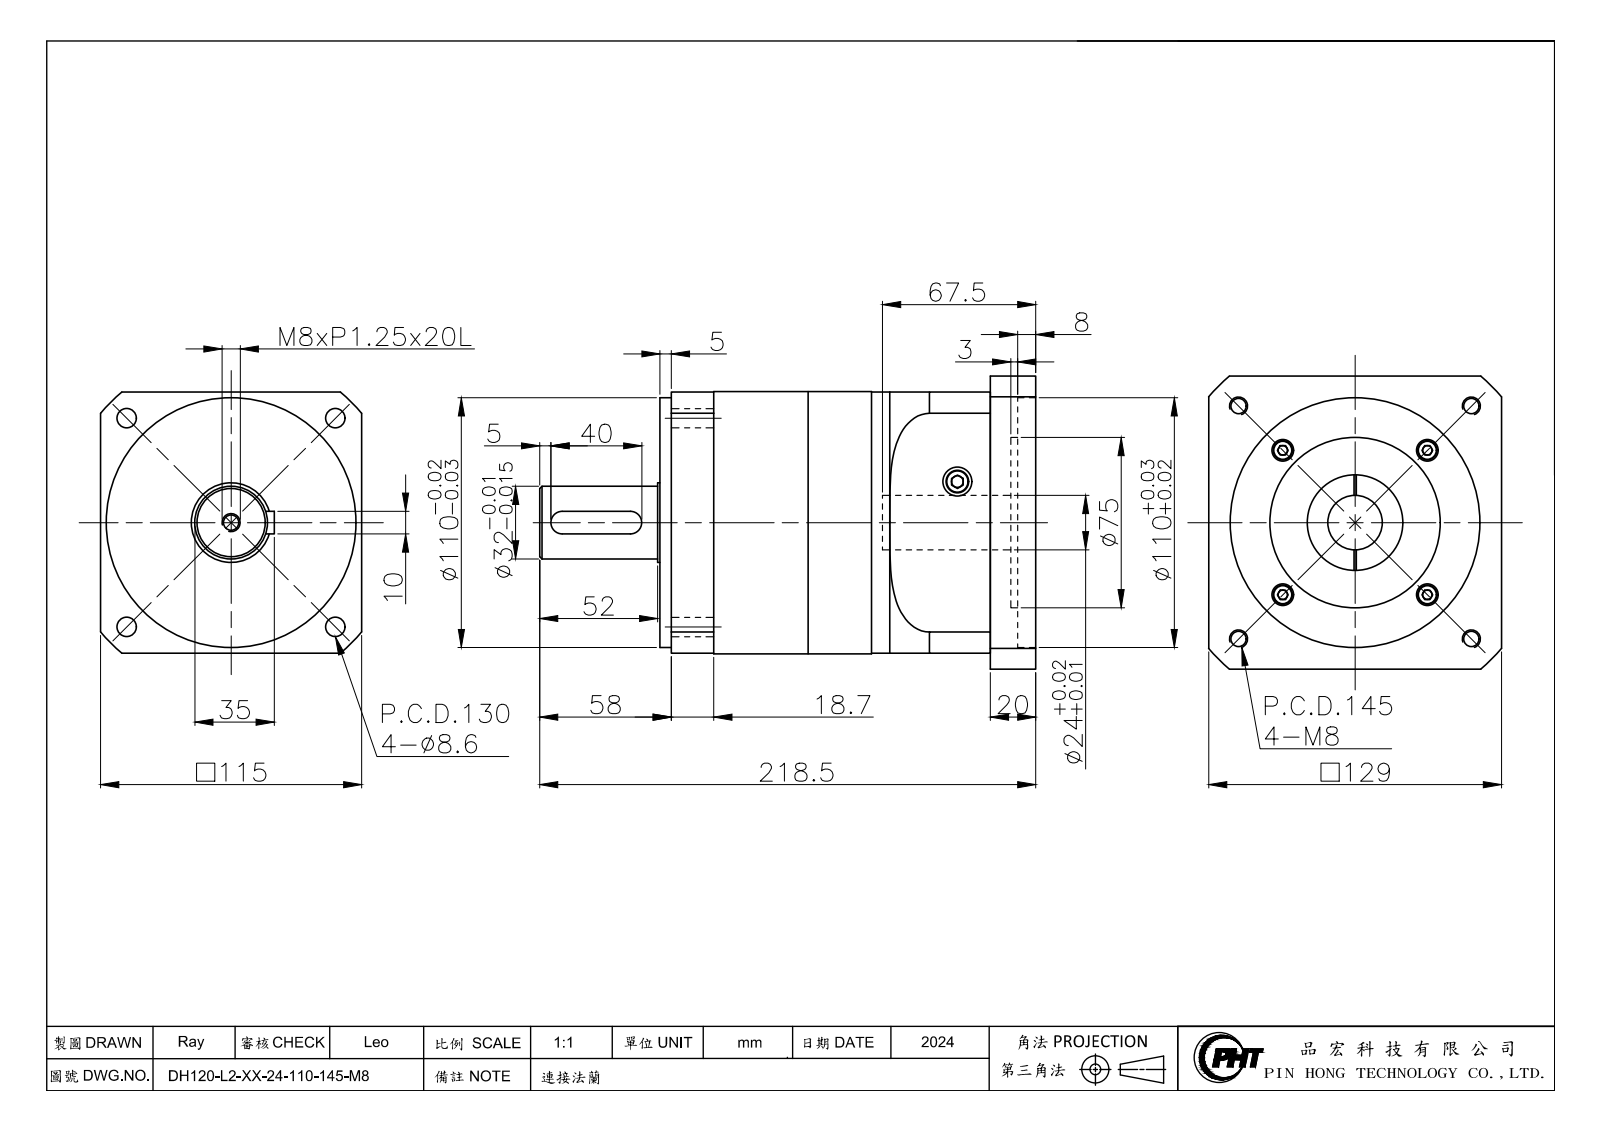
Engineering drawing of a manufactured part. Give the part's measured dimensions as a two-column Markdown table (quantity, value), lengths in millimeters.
| quantity | value |
| --- | --- |
| part name | DH120-L2-XX-24-110-145-M8(連接法蘭)_2024 |
| STEP written by | SolidWorks 2016 (CONFIG_CONTROL_DESIGN) |
| units | millimeters |
| bodies | 20 solids, 395 faces (174 planar, 157 cylindrical, 64 other) |
| overall size | 218.5 × 129 × 129 |
| volume | 1 845 000 mm³ |
| surface area | 247 082 mm² |
| round holes (diameter × count) | 9.5 × 8, 6.8 × 5, 4.2 × 4, 5.5 × 4, 8.6 × 4, 10 × 4, 12.7 × 2, 24 × 1, 42 × 1, 60 × 1, 70 × 1, 75 × 1 |
| round bosses / shafts (diameter × count) | 8.5 × 12, 5 × 12, 115.5 × 1, 115 × 1, 49 × 1, 35 × 1, 32 × 1 |
| partial cylindrical surfaces (radius × count) | 5 × 2, 75 × 1, 85 × 1 |
| main face-to-face distances | 41.5, 28, 69.5, 121.8, 80.3, 52.3, 115, 145.5, 93.2, 65.2 |
| hole center spacings | 21.24, 25.6, 30.64, 54, 55.5, 66.74, 71.94, 76.37 |
